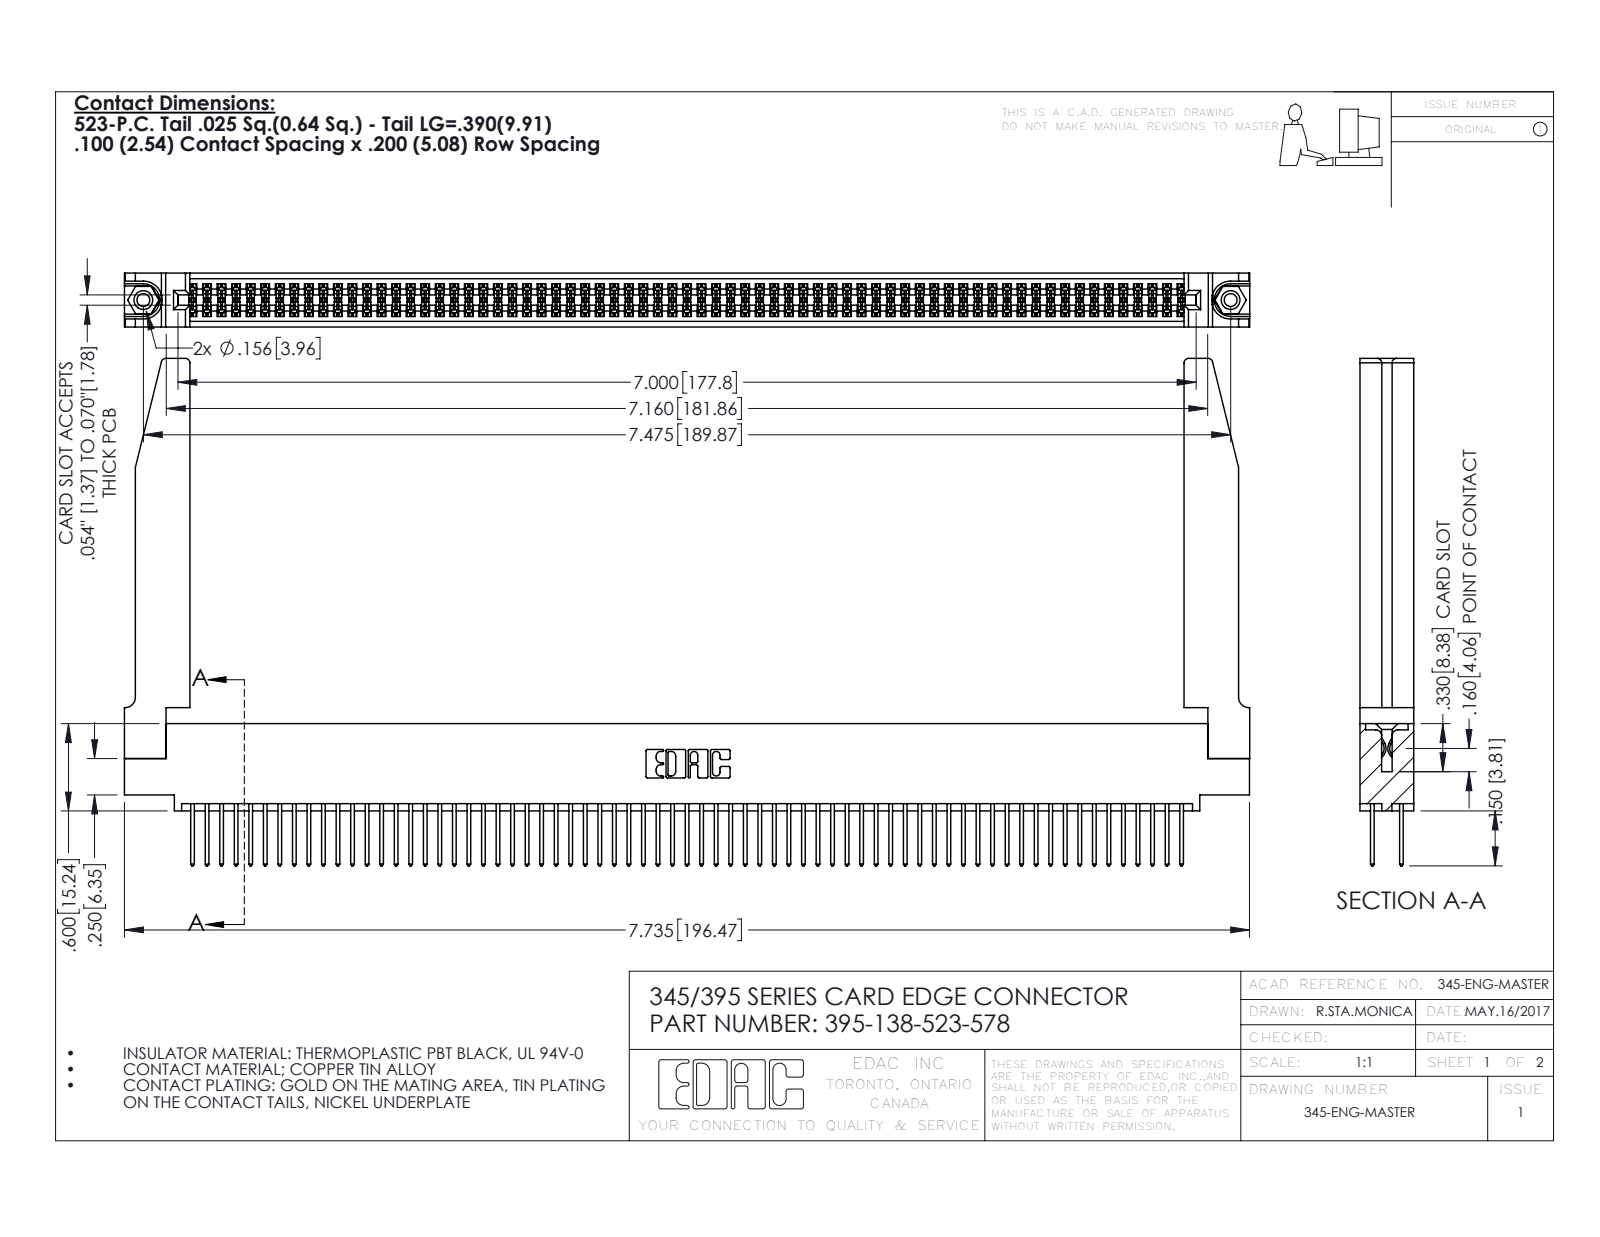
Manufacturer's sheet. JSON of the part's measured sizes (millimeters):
{"part_name": "345-292-001_345-293-123; 345 Part_0.110 Offset - 0.156 Dia-TH; 395-138-523-578; 345-250-001_345-250-001-102 (+1 more)", "step_written_by": "SolidWorks 2016 (CONFIG_CONTROL_DESIGN)", "units": "millimeters", "bodies": {"solids": 143, "faces": 7264, "planar": 4780, "cylindrical": 2432, "other": 52}, "overall_size": [196.5, 88.6, 9.4], "volume_mm3": 27320, "surface_area_mm2": 37620, "round_holes": [[2.3, 2], [3.2, 2], [4, 2], [1.6, 1]], "round_bosses_or_shafts": [[3.9, 2]], "partial_cylinders_radius": [[0.2, 207], [0.3, 138], [0.3, 22], [0.8, 8], [0.2, 6], [0.8, 6], [0.7, 3], [0.4, 2]], "face_to_face_distances": [1.8, 7.6, 9.4, 2.5, 6.9, 0.6, 5.1, 5.7, 4.4, 3.8], "hole_center_spacings": [6.9, 183.9, 189.9]}
